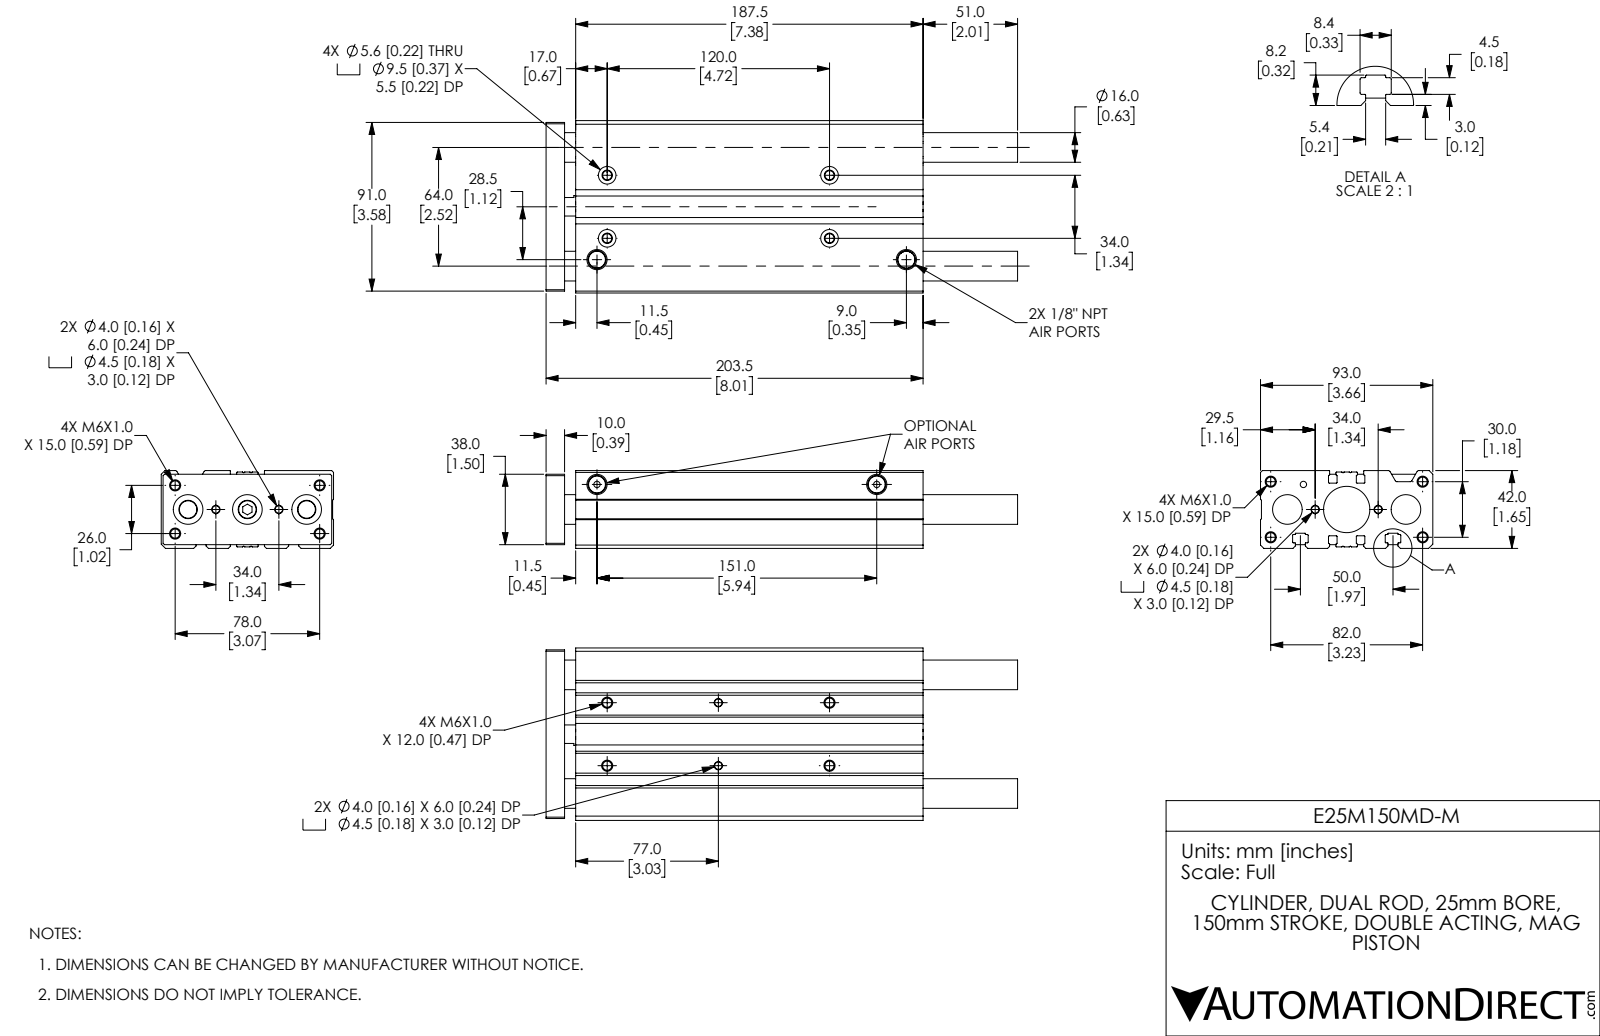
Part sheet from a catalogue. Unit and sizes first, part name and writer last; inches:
Units: inches
Overall size (bounding box): 10.02 × 3.661 × 1.654
Round holes (diameter × count): ⌀0.194 ×10, ⌀0.157 ×4, ⌀0.177 ×4, ⌀0.22 ×4, ⌀0.374 ×4, ⌀0.315 ×3, ⌀0.63 ×3, ⌀0.135 ×2, ⌀0.194 ×2, ⌀0.39 ×2, ⌀0.135 ×1, ⌀0.63 ×1
Round bosses / shafts (diameter × count): ⌀0.472 ×1, ⌀0.39 ×1
Partial cylindrical surfaces — rounded edges, fillets, slot ends (radius × count): R0.008 ×32, R0.016 ×28, R0.039 ×4, R0.012 ×2
Main face-to-face distances: 1.654, 0.236, 3.661, 0.031, 1.354, 0.591, 1.386, 1.622, 0.63, 0.268
Hole centre spacings: 0.111, 0.581, 0.689, 1.006, 1.105, 1.114, 1.339, 1.619
Volume: 40.17 in³ · Surface area: 250.3 in²
Bodies: 5 solids, 423 faces (139 planar, 190 cylindrical, 94 other)
Part name (STEP PRODUCT): E25M150MD-M_ENDPLATE; E25M150MD-M; E25M150MD-M_BODY
STEP written by: SolidWorks 2019 (CONFIG_CONTROL_DESIGN)
